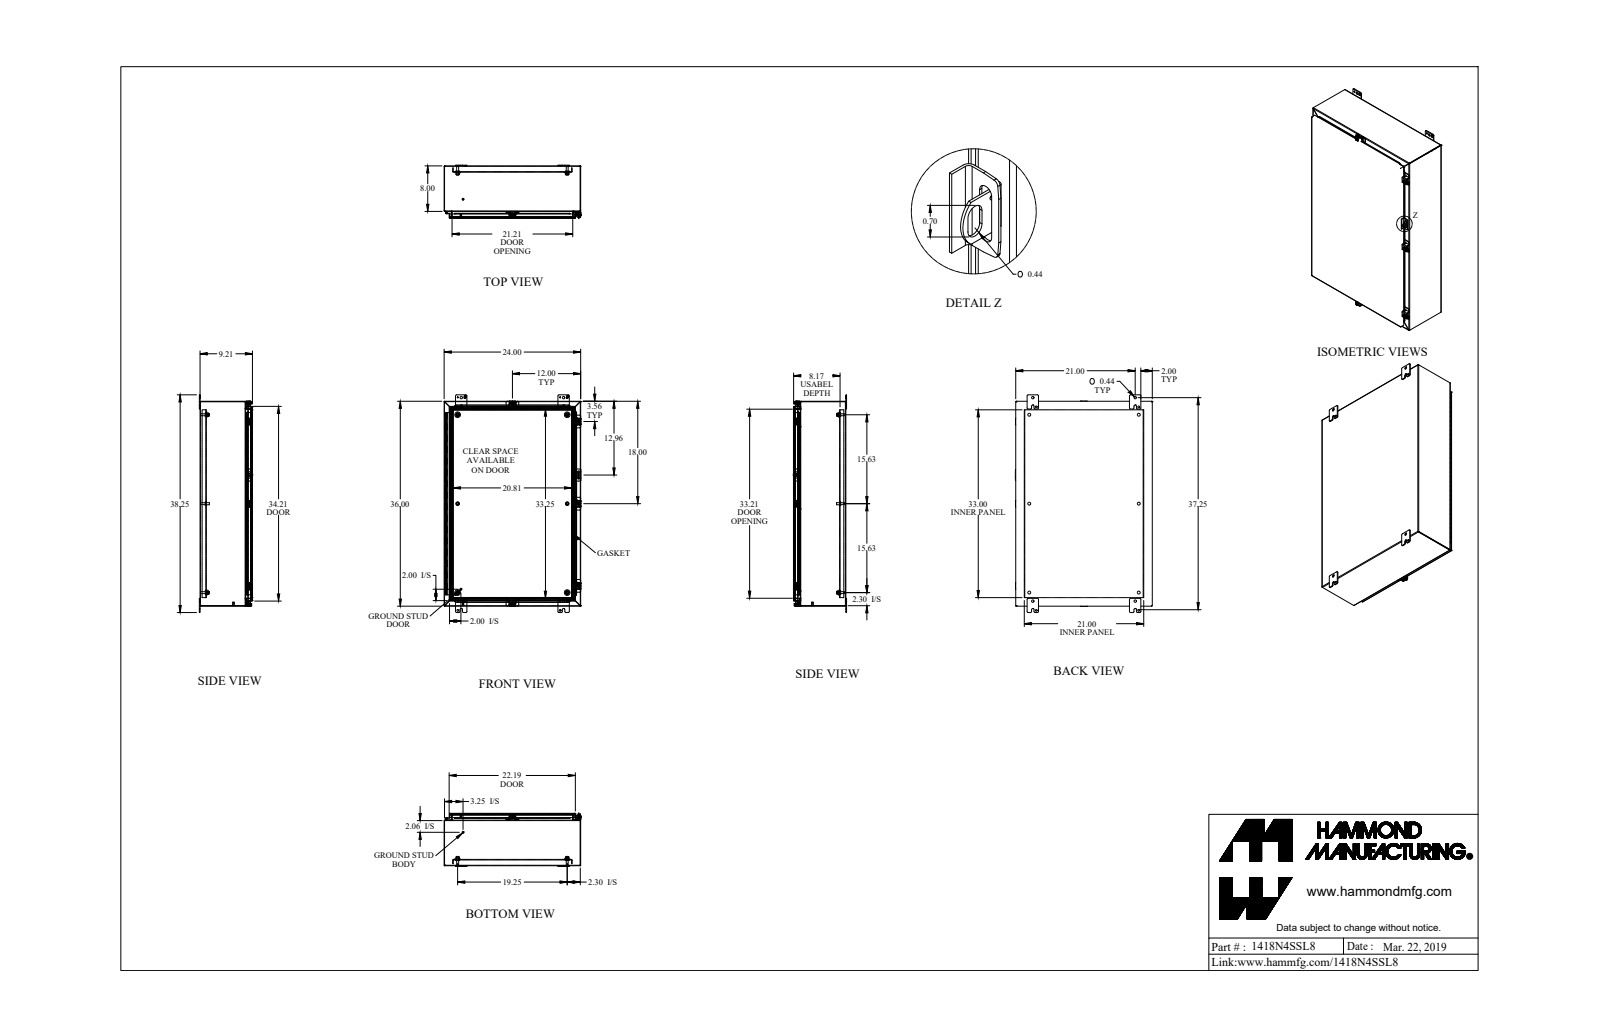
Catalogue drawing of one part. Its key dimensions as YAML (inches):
part_name: "1418N4SSL8_Default"
step_written_by: "SolidWorks 2019 (CONFIG_CONTROL_DESIGN)"
units: inches
bodies: {solids: 49, faces: 1809, planar: 1089, cylindrical: 614, other: 106}
overall_size: [38.25, 24.063, 9.375]
volume: 303.3
surface_area: 7938
round_holes:
  - {diameter: 0.5, count: 6}
  - {diameter: 0.213, count: 5}
  - {diameter: 0.265, count: 5}
  - {diameter: 0.375, count: 5}
  - {diameter: 0.307, count: 4}
  - {diameter: 0.313, count: 4}
  - {diameter: 0.437, count: 4}
  - {diameter: 0.445, count: 4}
  - {diameter: 0.125, count: 1}
  - {diameter: 0.187, count: 1}
round_bosses_or_shafts:
  - {diameter: 0.65, count: 6}
  - {diameter: 0.375, count: 6}
  - {diameter: 0.332, count: 6}
  - {diameter: 0.5, count: 5}
  - {diameter: 0.39, count: 5}
  - {diameter: 0.244, count: 5}
  - {diameter: 1, count: 4}
  - {diameter: 0.313, count: 2}
partial_cylinders:
  - {radius: 0.048, count: 27}
  - {radius: 0.143, count: 27}
  - {radius: 0.188, count: 26}
  - {radius: 0.036, count: 24}
  - {radius: 0.108, count: 24}
  - {radius: 0.25, count: 24}
  - {radius: 0.125, count: 10}
  - {radius: 0.141, count: 10}
face_to_face_distances: [0.072, 0.072, 9.066, 9.138, 9.138, 9.21, 0.095, 0.937, 1.009, 8.106]
hole_center_spacings: [15.625, 19.25, 34.735, 9.857, 31.25, 15.769, 18, 20.192]
